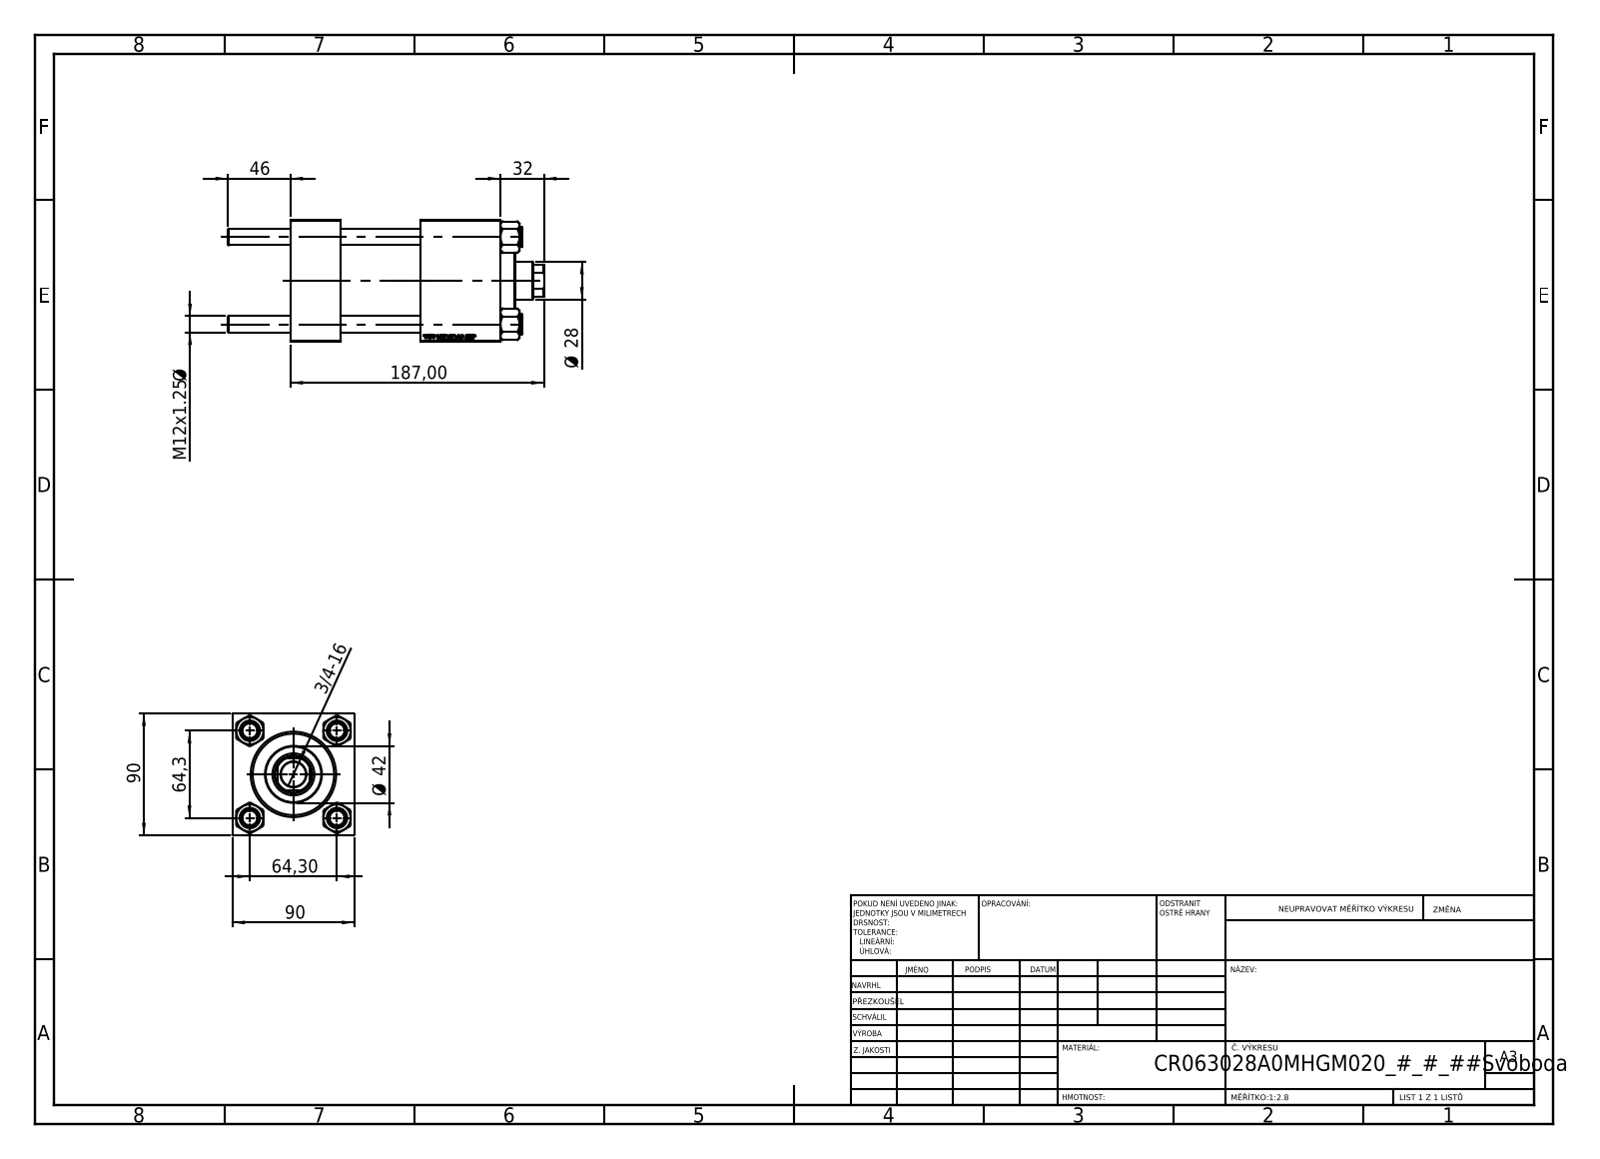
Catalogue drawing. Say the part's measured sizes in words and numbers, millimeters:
The part is named "V215_VC_A; CR025_012_A_0_G_A_G_M_020_+#_##_TYCINKA; V215CR_BODY_A; NUT_M5 (+1 more)". Its 3-D file was written by "SolidWorks 2019 (CONFIG_CONTROL_DESIGN)". It is 11 solids with 1134 faces: 520 planar, 78 cylindrical and 536 other. Overall it measures 233 by 90 by 90 millimeters. Its volume is 981 287 cubic millimeters and its surface area 195 264 square millimeters. Round holes: 4 of diameter 12, 2 of diameter 7, 2 of diameter 20.96, 2 of diameter 30, 1 of diameter 18.5, 1 of diameter 28, 1 of diameter 31, 1 of diameter 50, 1 of diameter 60, 1 of diameter 63. Round bosses or shafts: 4 of diameter 15, 1 of diameter 69, 1 of diameter 42. Partial cylindrical surfaces (rounded edges, fillets, slot ends): 1 of radius 13.5. The main face-to-face distances are 90, 59, 37, 155, 118, 96, 126.3, 89.3, 30.3, 28.7. The hole center spacings are 45.47, 64.3, 90.93, 97.5.
